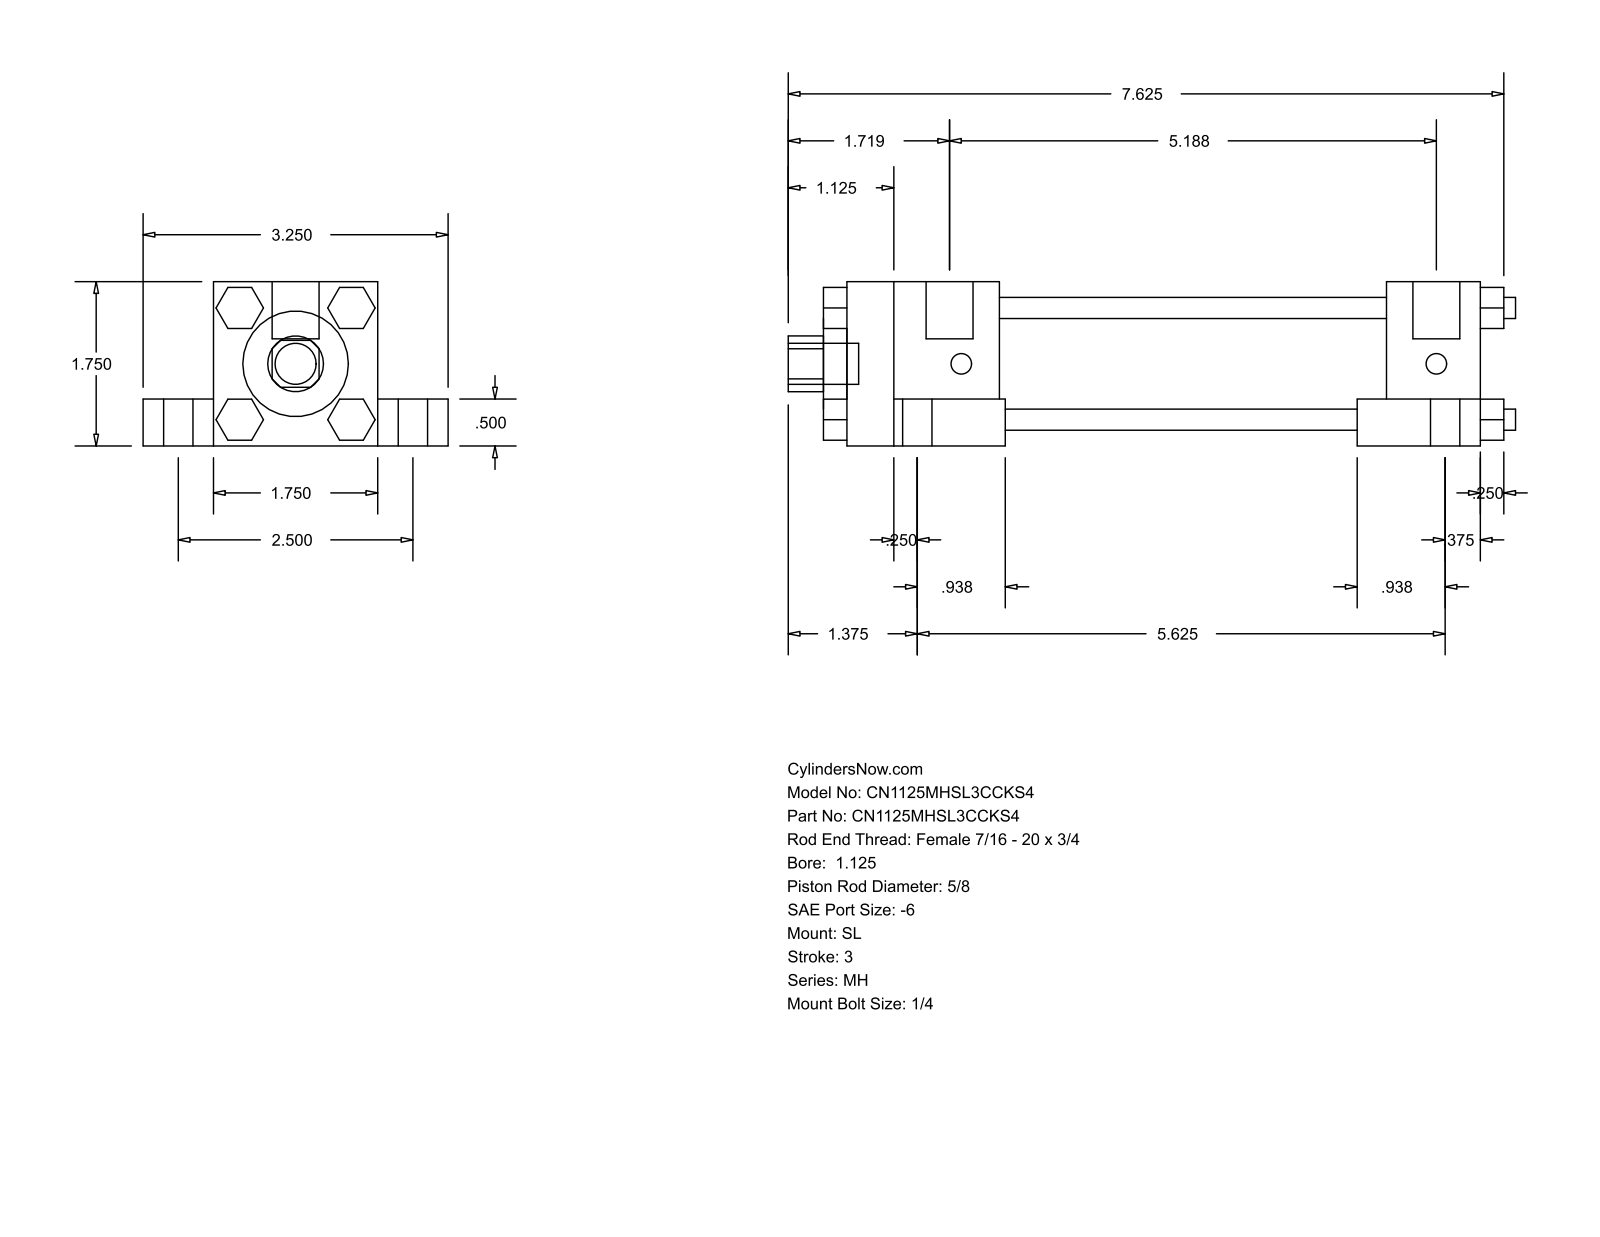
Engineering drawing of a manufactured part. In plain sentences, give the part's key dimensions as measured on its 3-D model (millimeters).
The part is named "MH_SL__0112_0.625". Its 3-D file was written by "GSSL Pune (CONFIG_CONTROL_DESIGN)". It is 0 solids with 150 faces: 114 planar, 36 cylindrical and 0 other. Overall it measures 196.85 by 82.55 by 44.45 millimeters. Round holes: 1 of diameter 15.88, 1 of diameter 28.57, 1 of diameter 34.92. Round bosses or shafts: 4 of diameter 14.29, 4 of diameter 7.94, 4 of diameter 5.71, 4 of diameter 5.56, 2 of diameter 12.7, 1 of diameter 11.11. Partial cylindrical surfaces (rounded edges, fillets, slot ends): 1 of radius 7.54. The main face-to-face distances are 44.46, 19.04, 12.7, 31.76, 63.5, 11.11, 104.78, 130.17, 25.39, 41.27.
